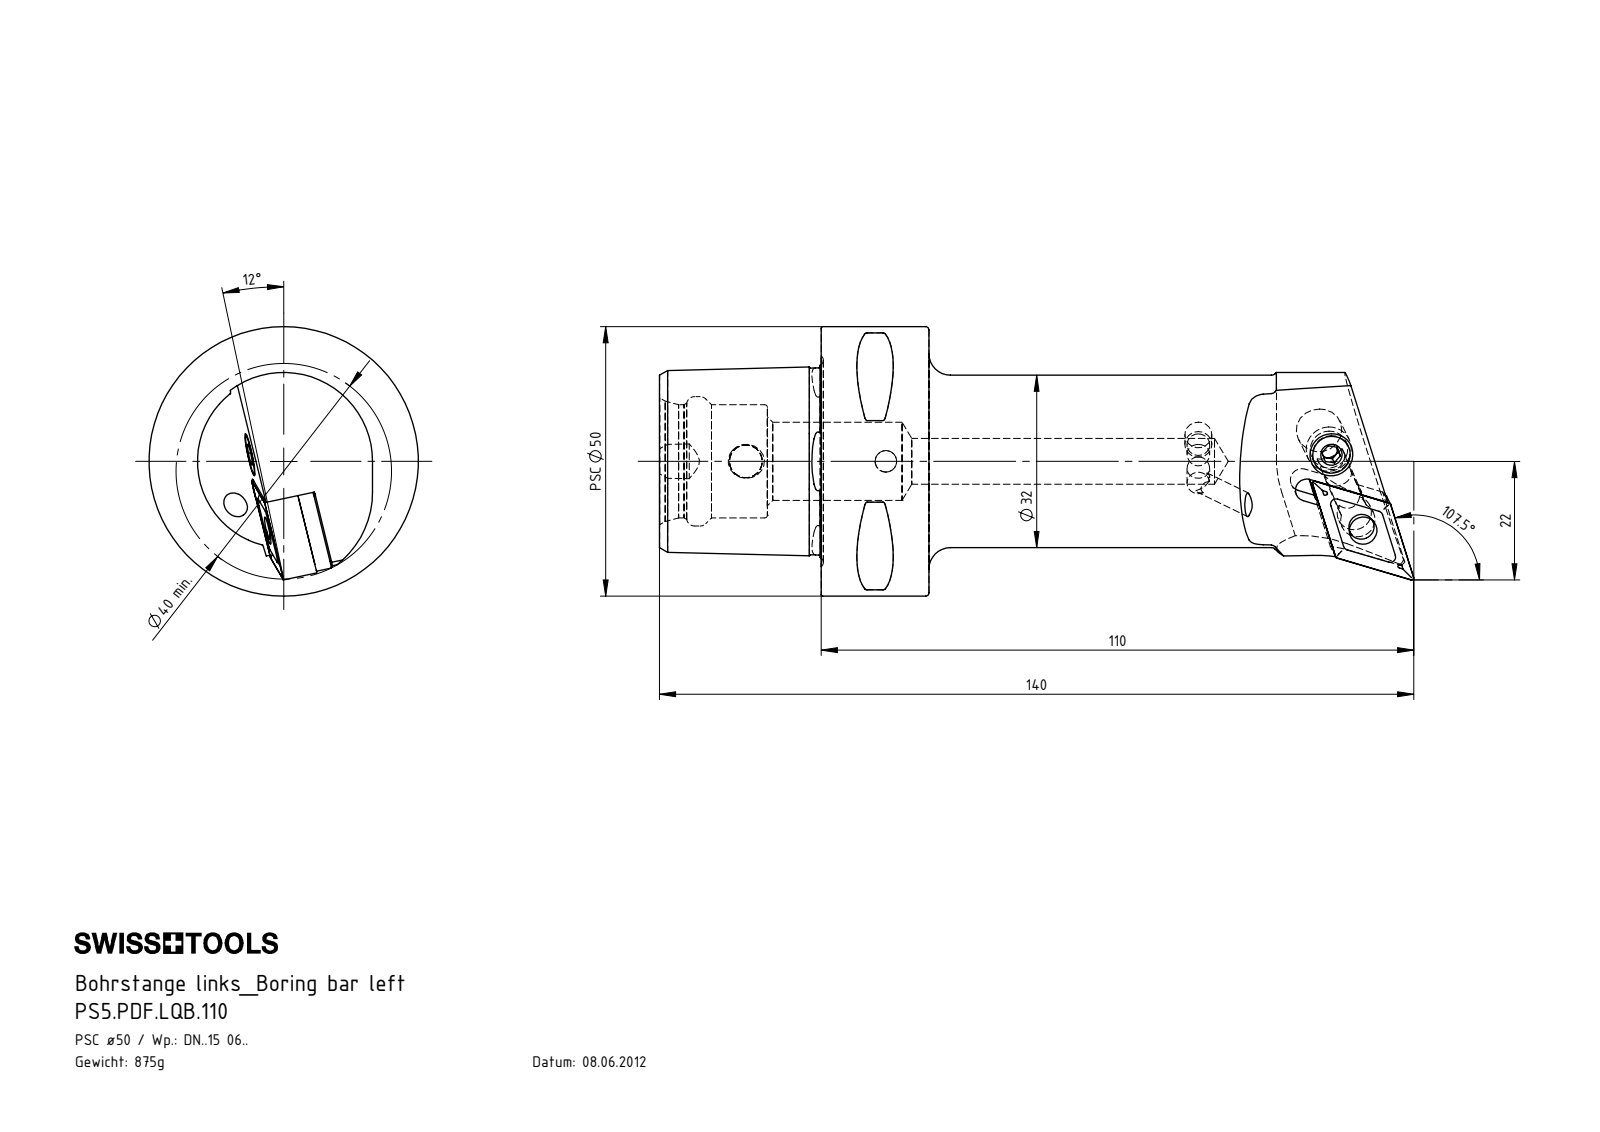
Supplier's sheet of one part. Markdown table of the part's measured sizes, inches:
| quantity | value |
| --- | --- |
| part name | KVT_MB_600_060; WDF-ER2.101.003_A; DNMG150604; WCD-ER1.101.000 (+4 more) |
| STEP written by | SolidWorks 2017 (AUTOMOTIVE_DESIGN) |
| units | inches |
| bodies | 8 solids, 350 faces (92 planar, 87 cylindrical, 171 other) |
| overall size | 5.512 × 1.969 × 1.969 |
| volume | 6.861 in³ |
| surface area | 41.4 in² |
| round holes (diameter × count) | 0.157 × 2, 0.165 × 1, 0.197 × 1, 0.203 × 1, 0.24 × 1, 0.252 × 1, 0.276 × 1, 0.331 × 1, 0.335 × 1, 0.571 × 1, 0.827 × 1, 0.945 × 1 |
| round bosses / shafts (diameter × count) | 1.969 × 1, 1.26 × 1, 0.315 × 1, 0.311 × 1, 0.252 × 1, 0.236 × 1, 0.185 × 1, 0.14 × 1 |
| partial cylindrical surfaces (radius × count) | 0.02 × 8, 0.016 × 4, 0.039 × 4, 0.098 × 2, 0.083 × 1, 0.093 × 1, 0.11 × 1, 0.118 × 1 |
| main face-to-face distances | 0.787, 1.181, 1.969, 0.238, 0.5, 0.755, 0.483, 0.017, 0.363, 0.125 |
| hole center spacings | 0.614, 1.024 |
